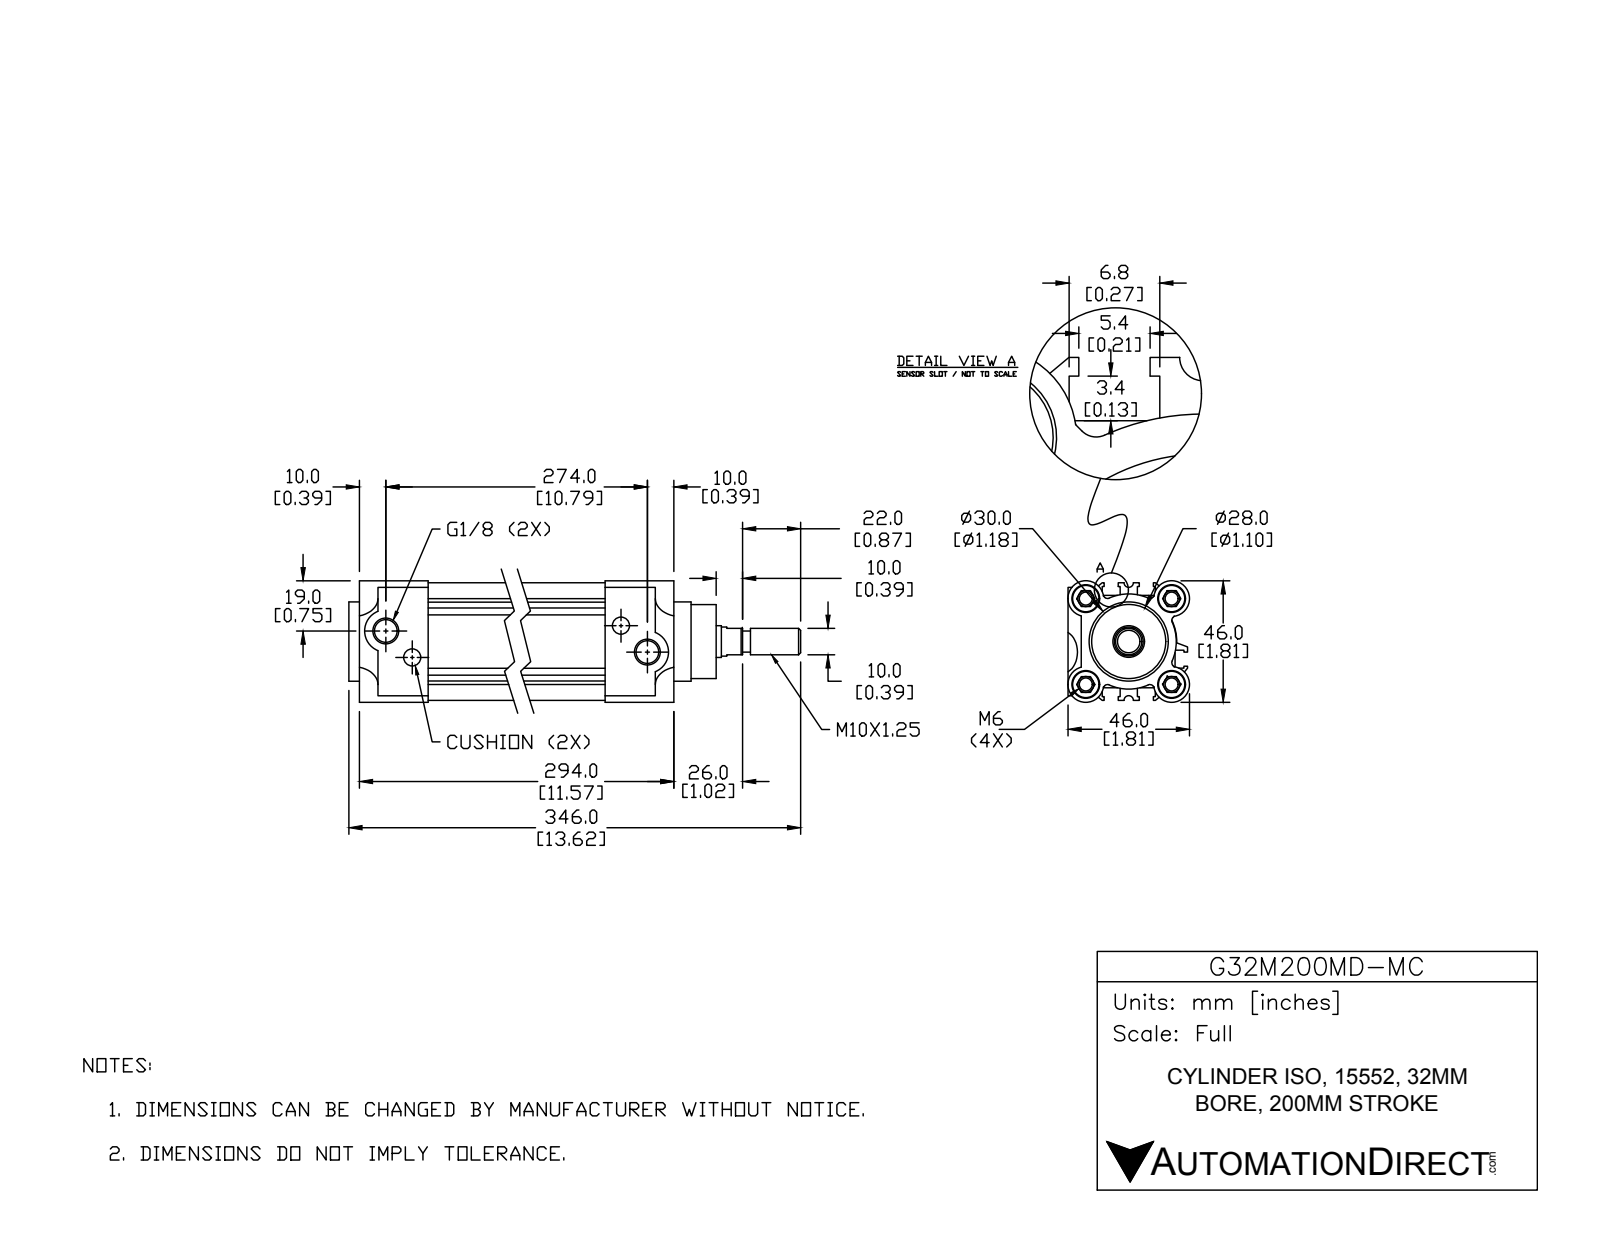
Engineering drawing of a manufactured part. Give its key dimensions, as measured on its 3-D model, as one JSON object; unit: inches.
{"part_name": "32-HL; G32M200MD-MC; 32121200-R; 32-200-73.5-B (+1 more)", "step_written_by": "SolidWorks 2015 (CONFIG_CONTROL_DESIGN)", "units": "inches", "bodies": {"solids": 4, "faces": 411, "planar": 229, "cylindrical": 138, "other": 44}, "overall_size": [13.622, 1.811, 1.811], "volume_in3": 22.4, "surface_area_in2": 211.5, "round_holes": [[0.194, 4], [0.413, 4], [0.256, 2], [0.337, 2], [0.472, 1]], "round_bosses_or_shafts": [[0.394, 5], [1.26, 1], [1.181, 1], [1.102, 1], [0.433, 1], [0.315, 1]], "partial_cylinders_radius": [[0.004, 12], [0.059, 6], [0.236, 4], [0.266, 4], [0.069, 2], [0.315, 2], [0.709, 1], [0.717, 1]], "face_to_face_distances": [1.565, 0.187, 1.004, 0.268, 1.378, 0.748, 0.48, 1.272, 1.752, 0.524], "hole_center_spacings": [0.905, 1.28, 0.557, 1.809, 10.394, 10.011, 10.792]}
